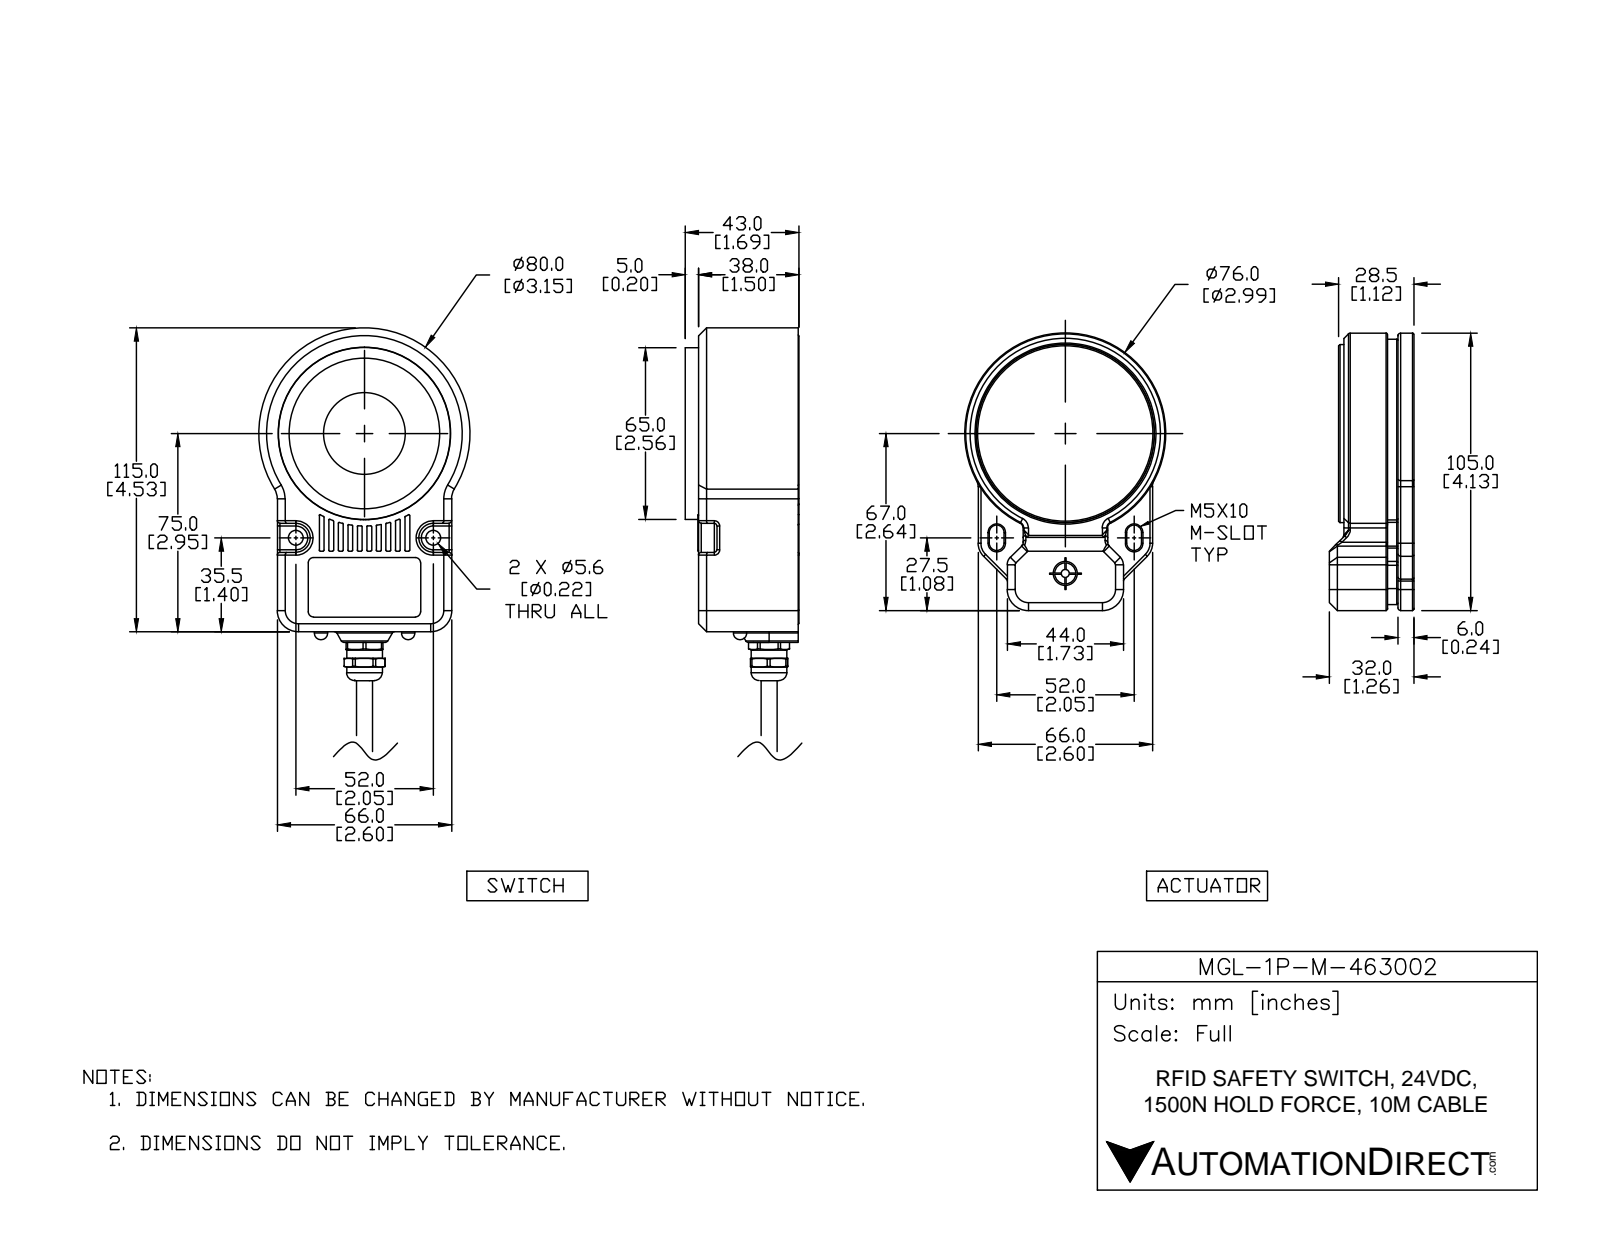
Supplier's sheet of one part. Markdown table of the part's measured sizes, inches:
| quantity | value |
| --- | --- |
| part name | MGL-1P-U-463002_1; MGL-1P-U-463002; MGL-1P-U-463002_2 |
| STEP written by | SolidWorks 2017 (AUTOMOTIVE_DESIGN) |
| units | inches |
| bodies | 17 solids, 1674 faces (449 planar, 708 cylindrical, 517 other) |
| overall size | 8.163 × 3.15 × 2.854 |
| volume | 18.96 in³ |
| surface area | 210.2 in² |
| round holes (diameter × count) | 0.197 × 6, 0.453 × 5, 0.094 × 4, 0.315 × 3, 0.079 × 2, 0.13 × 2, 0.22 × 2, 0.276 × 2, 0.354 × 2, 0.157 × 1, 0.252 × 1, 0.266 × 1 |
| round bosses / shafts (diameter × count) | 0.02 × 4, 0.472 × 3, 0.079 × 3, 0.228 × 2, 0.213 × 2, 0.154 × 2, 0.047 × 2, 2.992 × 1 |
| partial cylindrical surfaces (radius × count) | 0.02 × 187, 0.039 × 75, 0.012 × 39, 0.079 × 18, 0.024 × 7, 0.315 × 7, 0.157 × 6, 0.217 × 6 |
| main face-to-face distances | 0.236, 0.315, 0.098, 2.303, 2.618, 0.413, 2.205, 0.118, 0.65, 2.854 |
| hole center spacings | 0.787, 0.984, 1.392, 1.364, 0.173, 0.349, 0.4, 0.406 |
